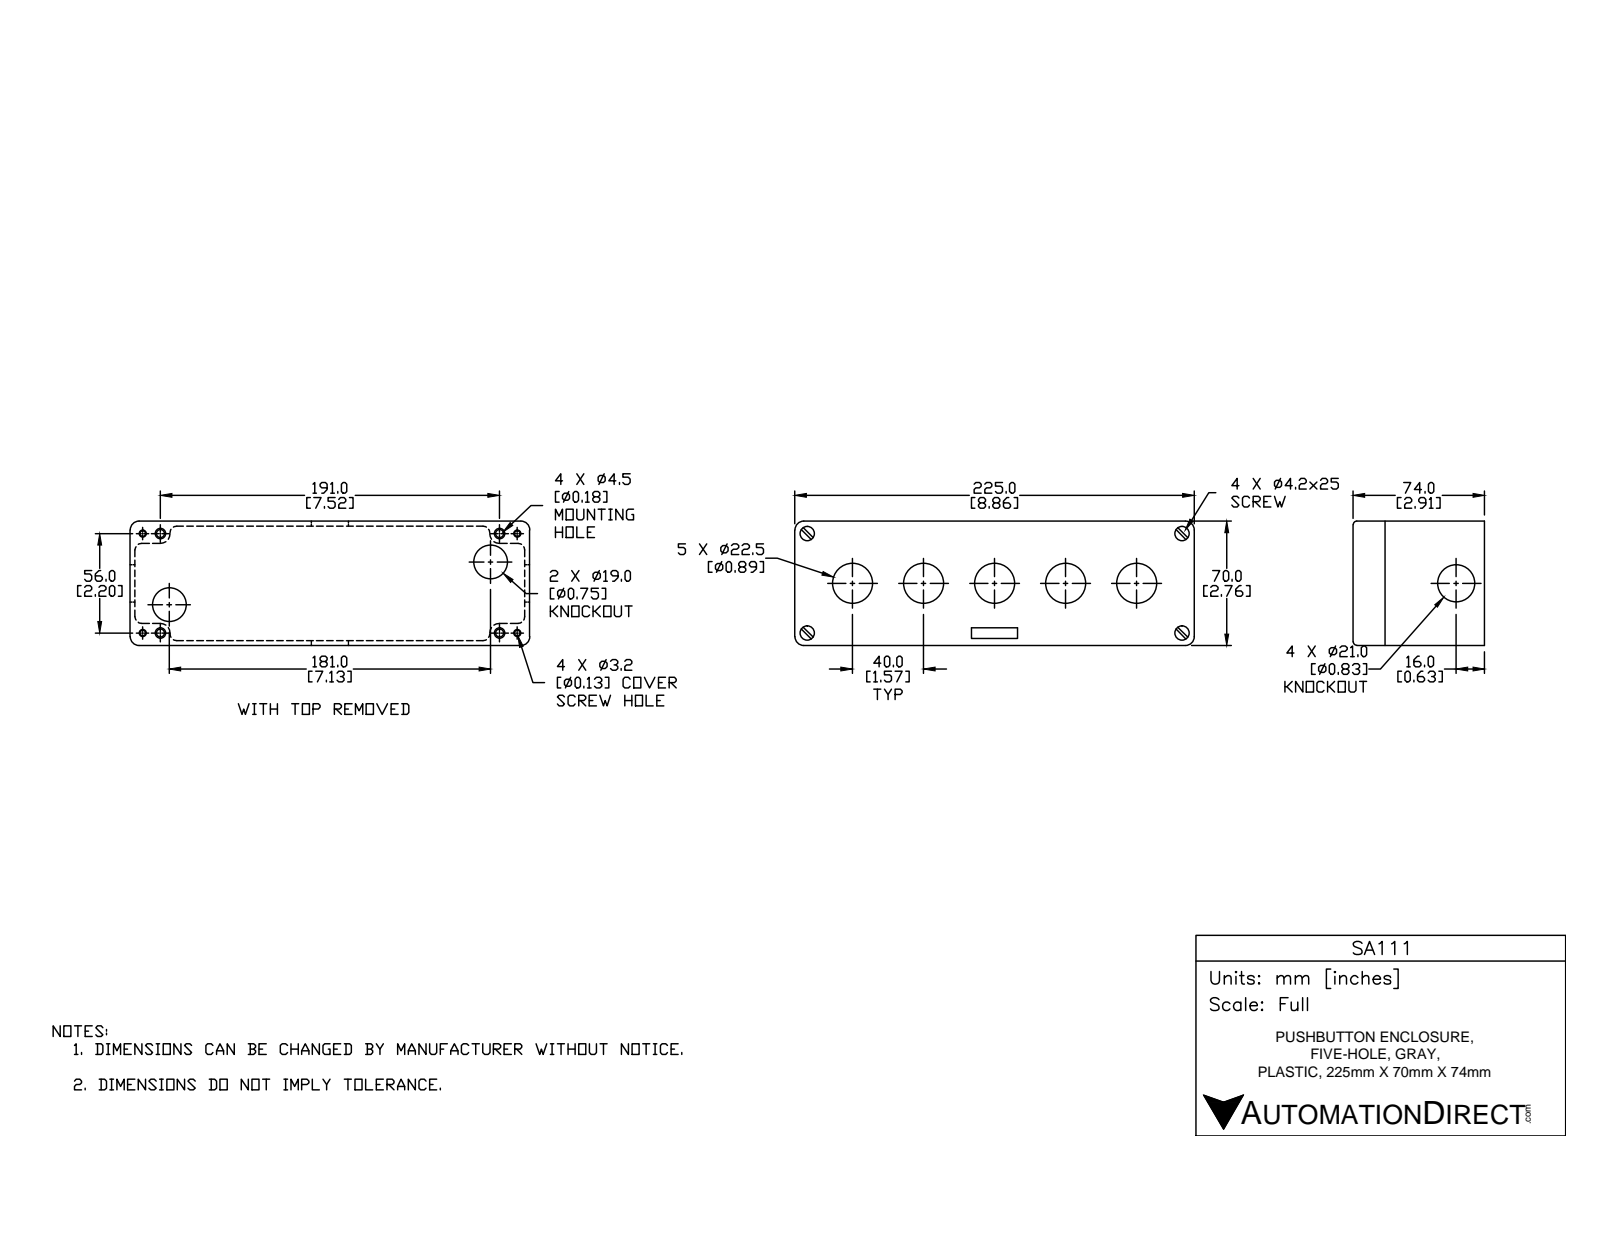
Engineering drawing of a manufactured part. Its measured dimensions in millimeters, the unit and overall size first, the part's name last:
Units: millimetres
Overall size (bounding box): 225 × 74 × 70
Round holes (diameter × count): ⌀22.5 ×5, ⌀3.2 ×4, ⌀4.3 ×4, ⌀4.5 ×4, ⌀7.5 ×4, ⌀8 ×4, ⌀2.4 ×2, ⌀19 ×2, ⌀21 ×2
Round bosses / shafts (diameter × count): ⌀7.4 ×4, ⌀2.8 ×4
Partial cylindrical surfaces — rounded edges, fillets, slot ends (radius × count): R0.5 ×16, R0.8 ×8, R3 ×8, R1 ×4, R1.8 ×4, R5 ×4, R6.3 ×4, R8.4 ×4
Main face-to-face distances: 70, 3.5, 2.5, 74, 71.6, 66.5, 3.5, 62.9, 66.5, 69.5
Hole centre spacings: 28.4, 201, 10, 32, 37.9, 40, 56, 56.9
Volume: 269 600 mm³ · Surface area: 148 500 mm²
Bodies: 6 solids, 497 faces (133 planar, 202 cylindrical, 162 other)
Part name (STEP PRODUCT): SA111
STEP written by: SolidWorks 2018 (AUTOMOTIVE_DESIGN)
